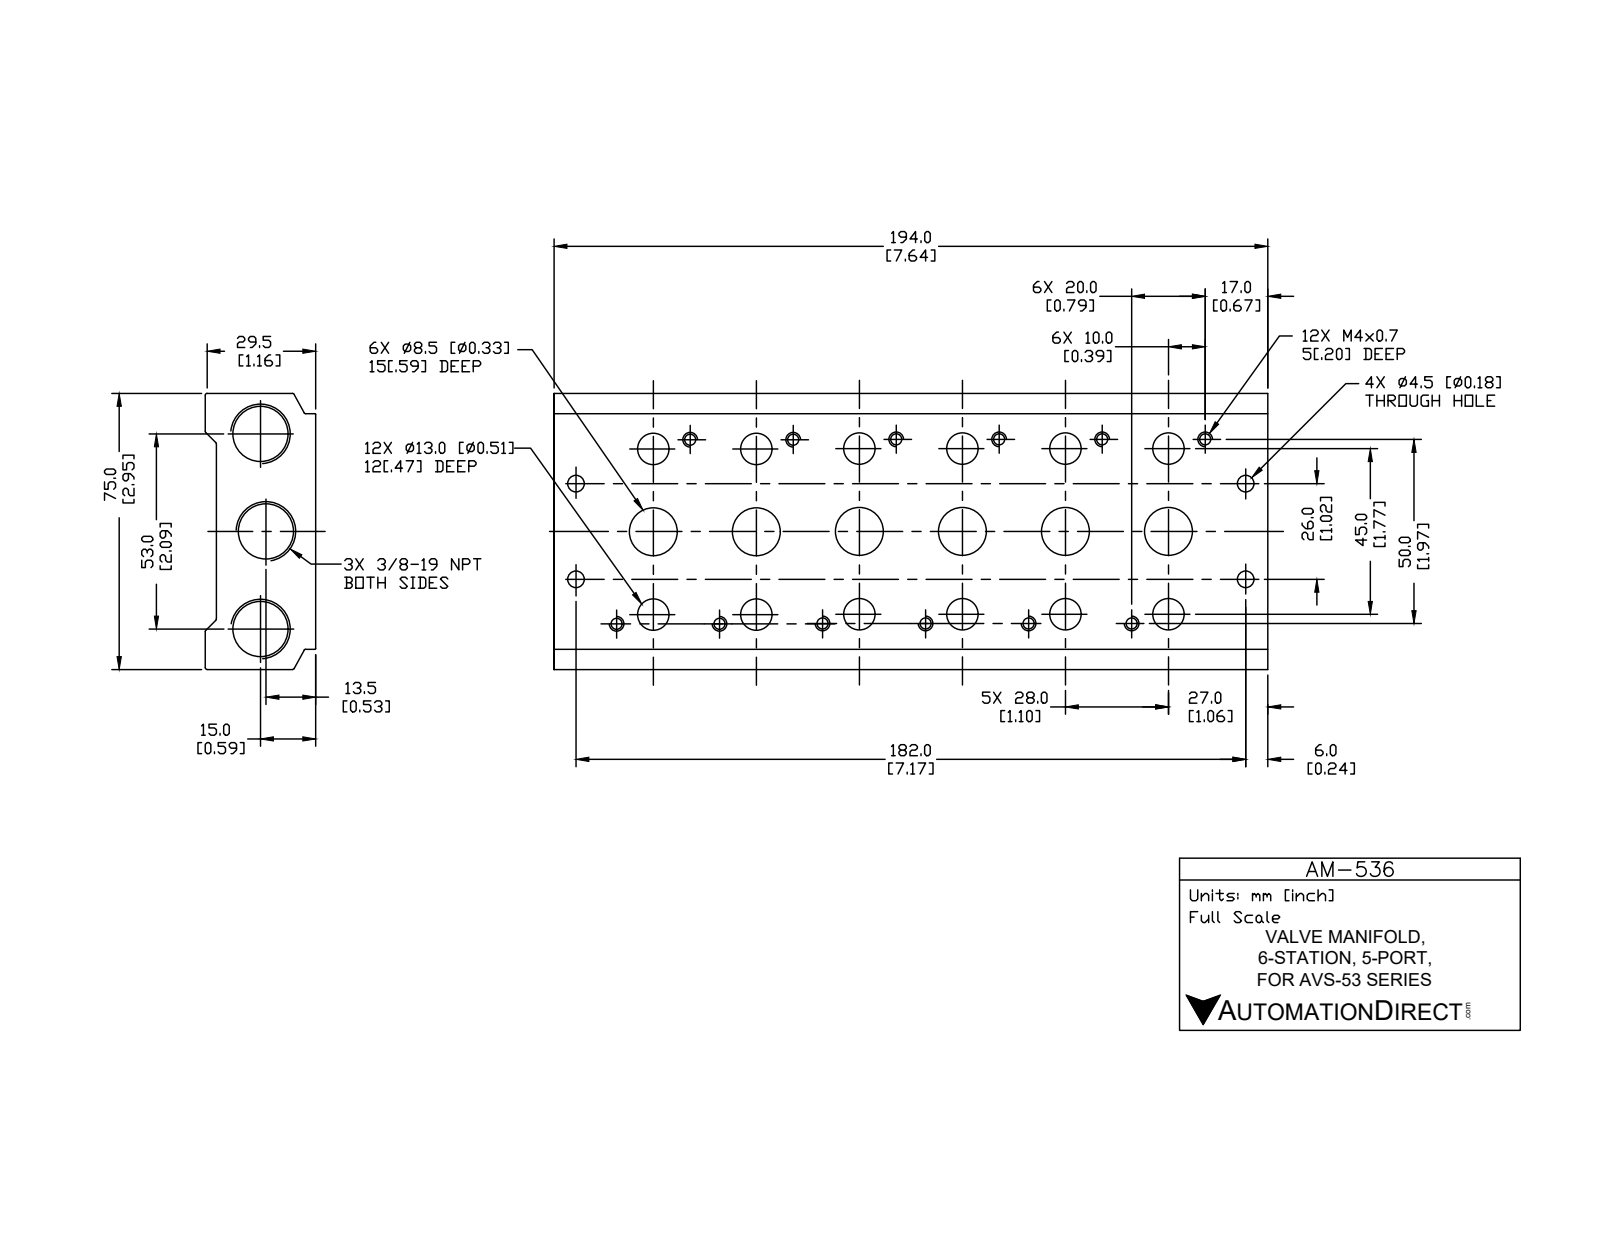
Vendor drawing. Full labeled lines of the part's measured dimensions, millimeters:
Part name (STEP PRODUCT): AM-536
STEP written by: SolidWorks 2015 (CONFIG_CONTROL_DESIGN)
Units: millimetres
Bodies: 1 solid, 165 faces (44 planar, 85 cylindrical, 36 other)
Overall size (bounding box): 194 × 75 × 30
Volume: 289 684 mm³ · Surface area: 74 528 mm²
Round holes (diameter × count): ⌀3.3 ×12, ⌀8.5 ×12, ⌀13 ×6, ⌀4.5 ×4, ⌀14.27 ×3
Partial cylindrical surfaces — rounded edges, fillets, slot ends (radius × count): R0.5 ×11
Main face-to-face distances: 27, 75, 3, 30, 194, 6, 69, 10.33, 183.67, 20
Hole centre spacings: 28, 35.92, 56, 84, 10.31, 22.5, 26.93, 48.54
